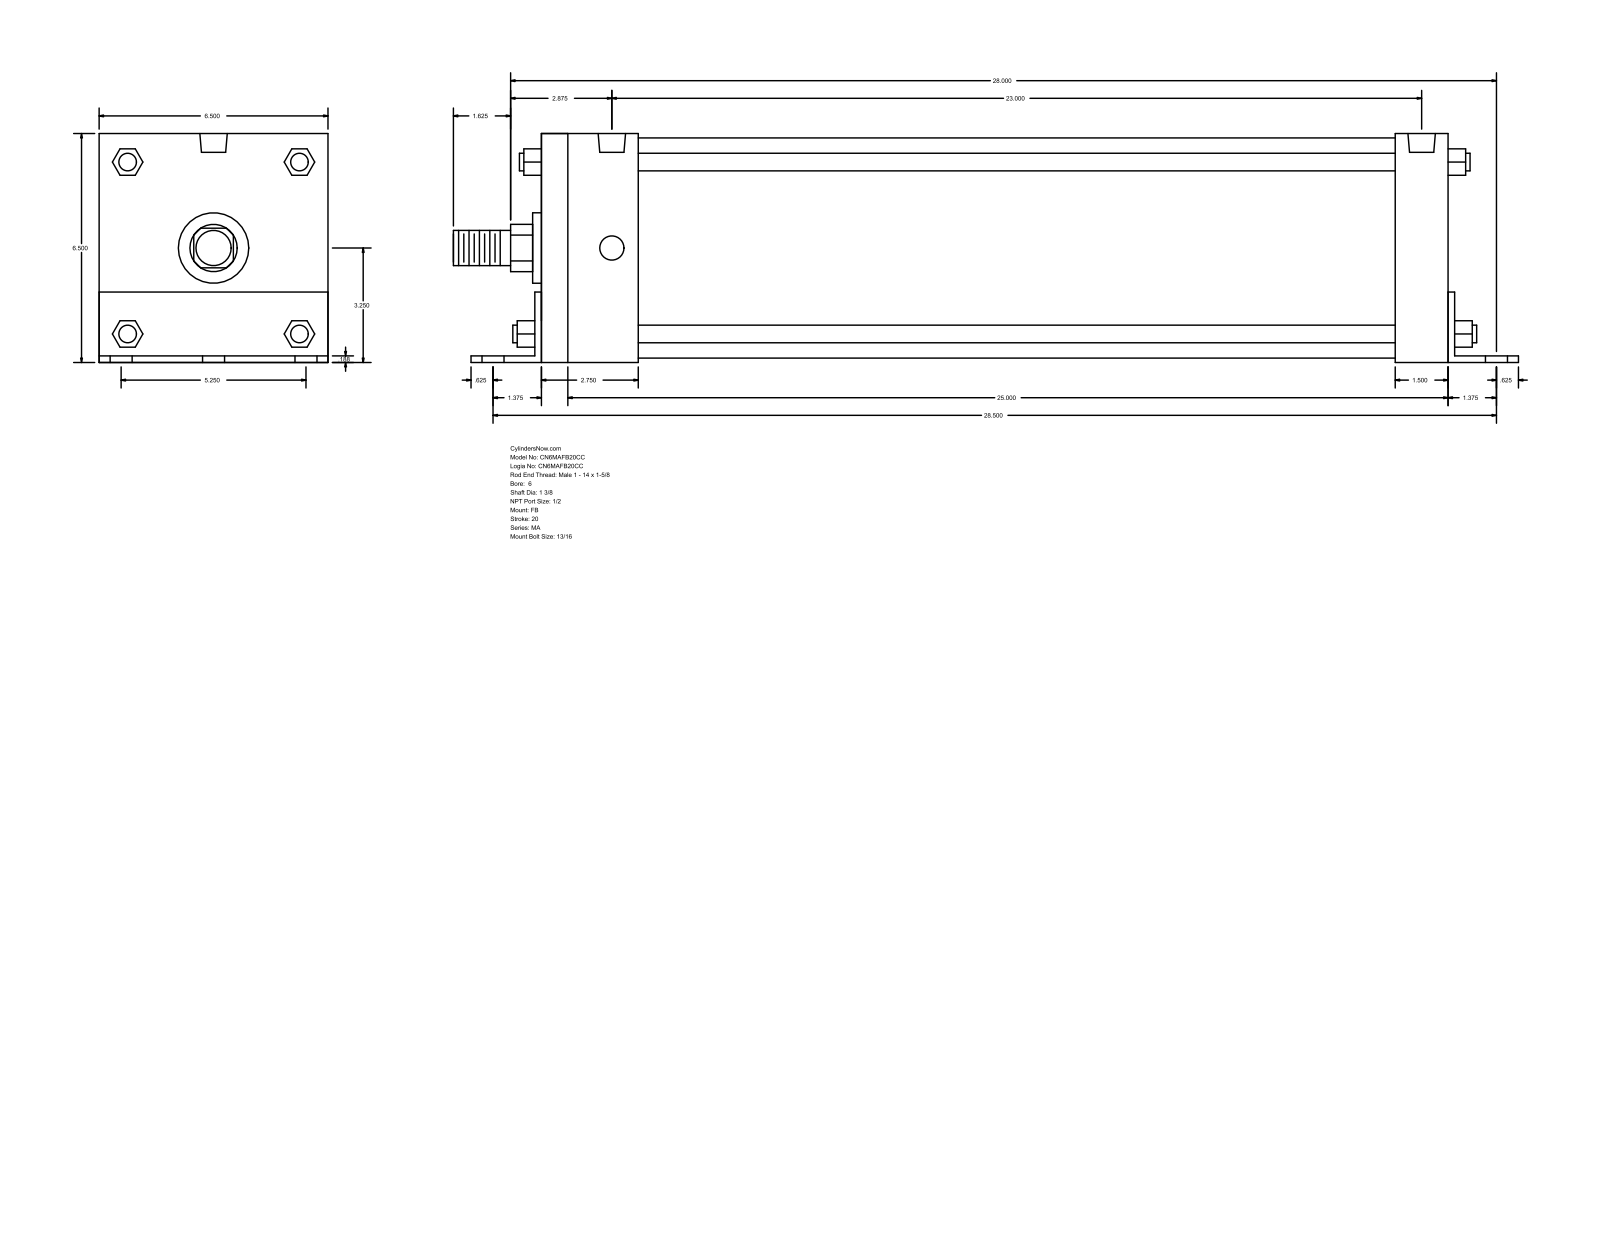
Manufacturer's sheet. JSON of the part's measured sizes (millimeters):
{"part_name": "MA_FB__0600_1.375", "step_written_by": "GSSL Pune (CONFIG_CONTROL_DESIGN)", "units": "millimeters", "bodies": {"solids": 0, "faces": 140, "planar": 105, "cylindrical": 35, "other": 0}, "overall_size": [765.17, 165.15, 165.1], "round_holes": [[20.64, 6], [17.46, 4], [19.77, 2]], "round_bosses_or_shafts": [[12.7, 4], [158.75, 1], [50.8, 1], [34.92, 1], [25.4, 1]], "partial_cylinders_radius": [[17.06, 1], [32.05, 1]], "face_to_face_distances": [165.1, 4.76, 650.87, 165.15, 4.71, 160.39, 4.77, 38.1, 42.86, 660.4], "hole_center_spacings": [66.67, 723.8, 720.72, 83.81, 85.78, 108.6, 133.34, 581.02]}
